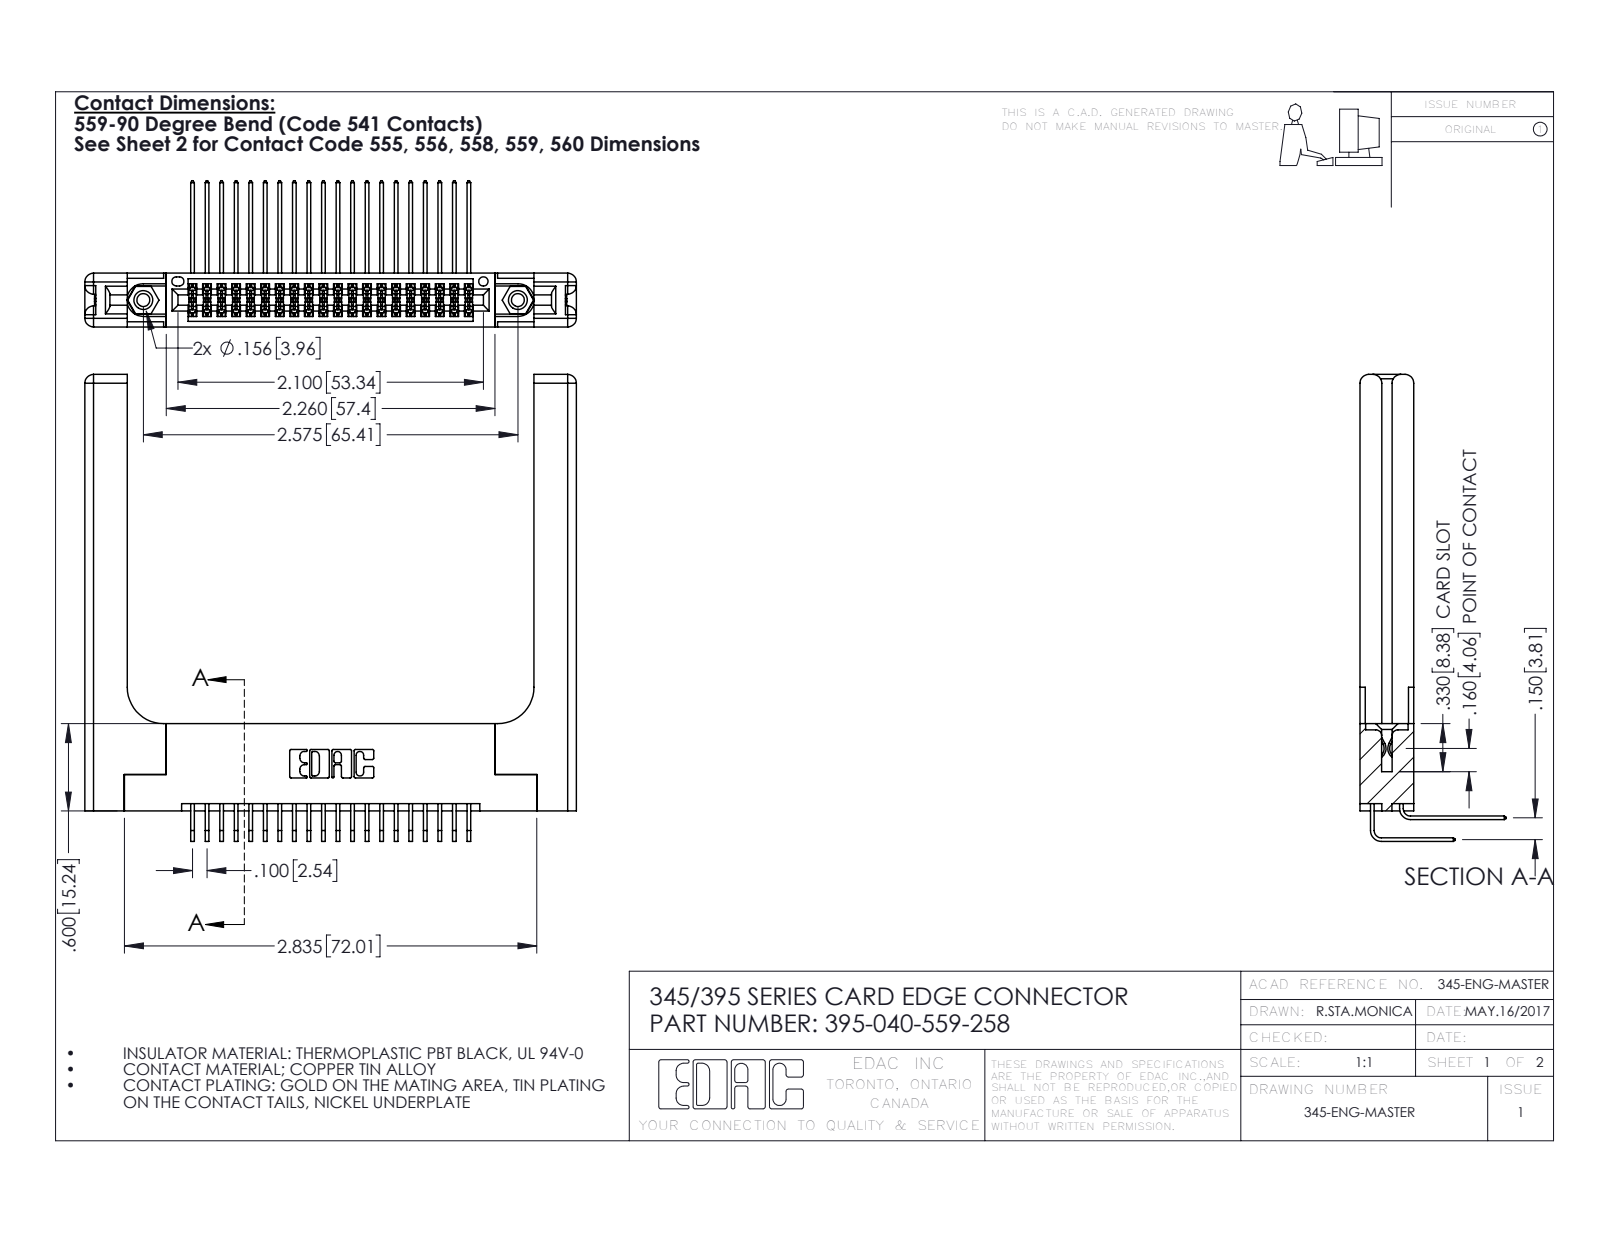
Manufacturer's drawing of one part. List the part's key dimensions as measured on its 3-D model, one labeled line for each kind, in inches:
Part name (STEP PRODUCT): 345-220-058_345-220-058; 345 Part_Flush Mounting Lugs - 0.156 Dia-TH; 345-292-001_558 559 Tail - 1; 345-250-001_345-250-001-102 (+2 more)
STEP written by: SolidWorks 2016 (CONFIG_CONTROL_DESIGN)
Units: inches
Bodies: 45 solids, 2462 faces (1628 planar, 774 cylindrical, 60 other)
Overall size (bounding box): 3.379 × 3.209 × 1.005
Volume: 1.028 in³ · Surface area: 28.03 in²
Round holes (diameter × count): ⌀0.089 ×2, ⌀0.125 ×2, ⌀0.156 ×2, ⌀0.064 ×1
Round bosses / shafts (diameter × count): ⌀0.155 ×2
Partial cylindrical surfaces — rounded edges, fillets, slot ends (radius × count): R0.006 ×61, R0.01 ×22, R0.06 ×16, R0.007 ×6, R0.031 ×6, R0.026 ×3, R0.014 ×2, R0.019 ×2
Main face-to-face distances: 0.37, 0.072, 0.298, 0.2, 0.148, 0.15, 0.077, 0.22, 0.098, 0.272
Hole centre spacings: 0.27, 2.341, 2.575
